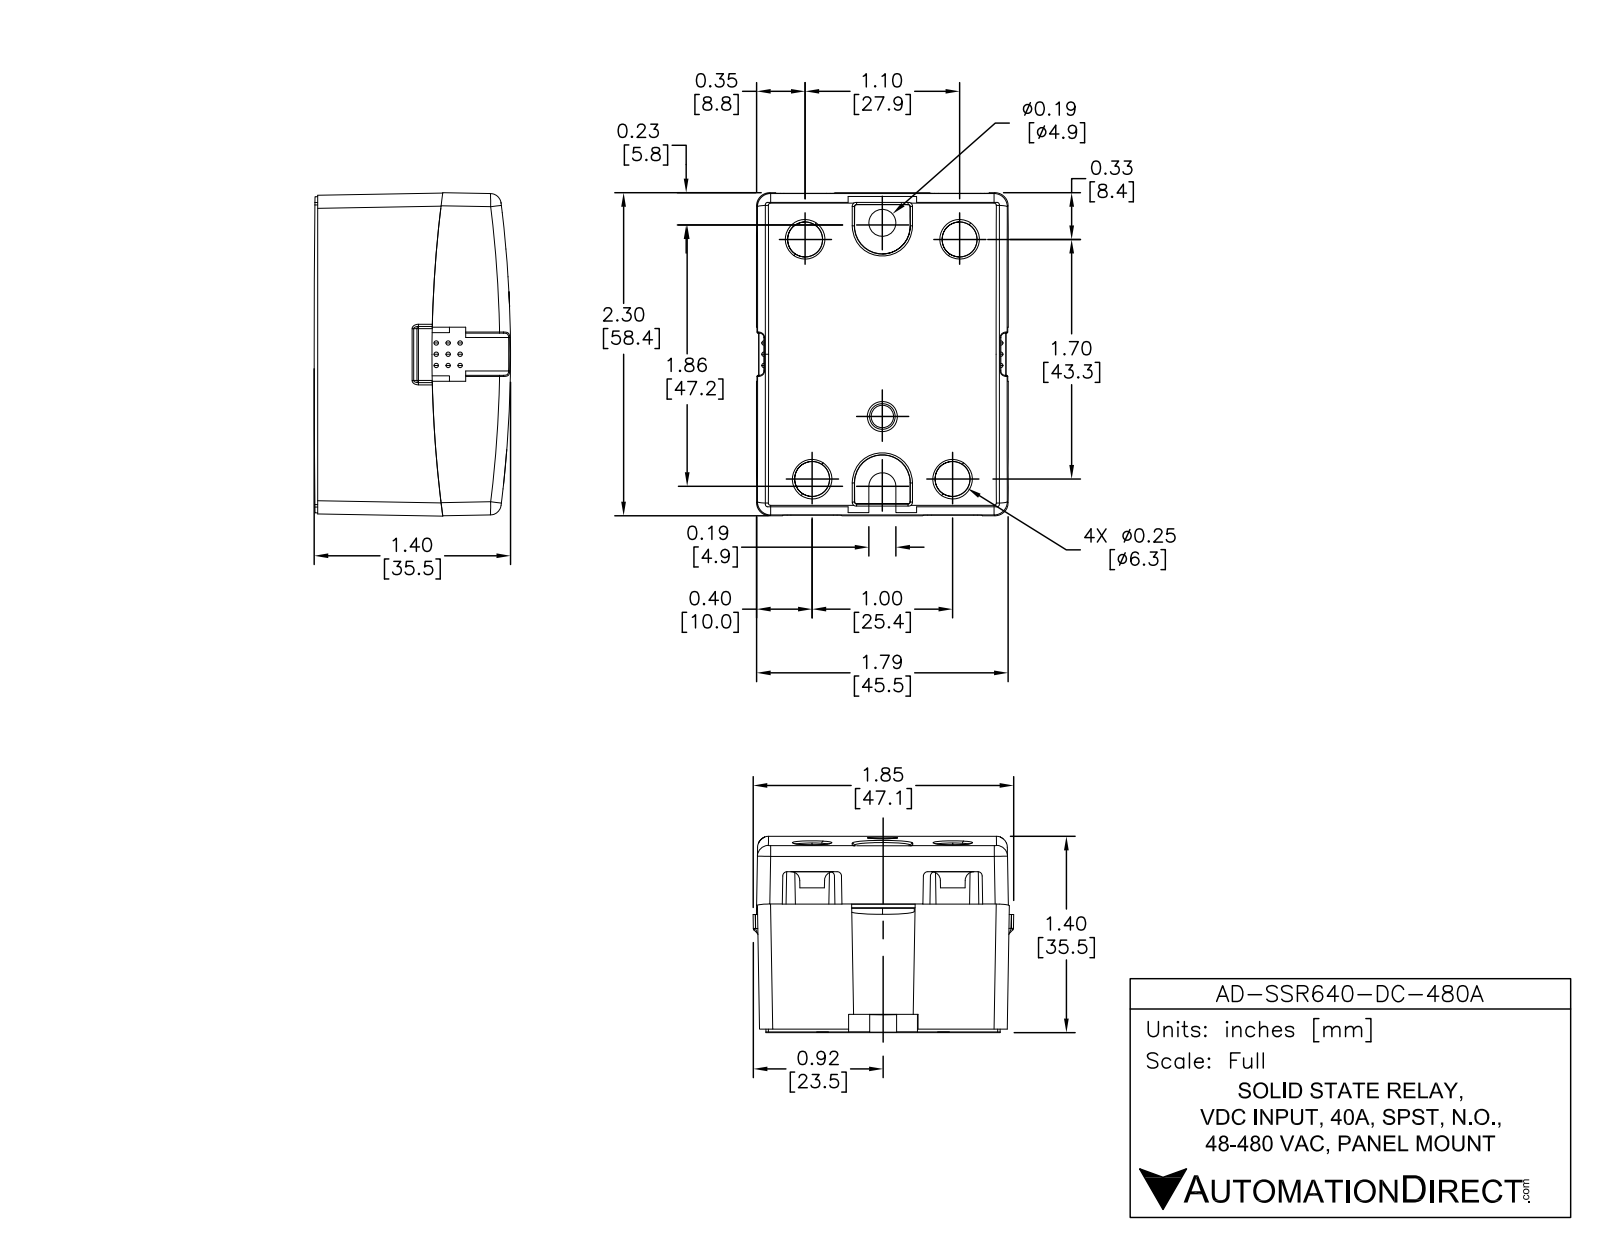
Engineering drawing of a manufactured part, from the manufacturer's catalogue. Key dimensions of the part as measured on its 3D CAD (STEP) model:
Part name (STEP PRODUCT): AD-SSR640-DC-480A
STEP written by: SolidWorks 2013 (AUTOMOTIVE_DESIGN)
Units: inches
Bodies: 3 solids, 251 faces (145 planar, 95 cylindrical, 11 other)
Overall size (bounding box): 2.3 × 1.79 × 1.4
Volume: 5.14 in³ · Surface area: 26.41 in²
Round holes (diameter × count): ⌀0.25 ×4, ⌀0.19 ×1
Round bosses / shafts (diameter × count): ⌀0.4 ×2, ⌀0.35 ×2, ⌀0.3 ×2, ⌀0.25 ×2, ⌀0.2 ×2, ⌀0.2 ×2
Partial cylindrical surfaces — rounded edges, fillets, slot ends (radius × count): R0.03 ×6, R0.01 ×4, R0.04 ×4, R0.5 ×4, R0.194 ×2, R0.095 ×1, R0.5 ×1, R0.5 ×1
Main face-to-face distances: 1.79, 2.3, 1.166, 0.25, 0.916, 0.671, 1.059, 0.5, 1.8, 0.08
Hole centre spacings: 0.556, 0.565, 1, 1.1, 1.7, 1.701, 1.876, 1.879
